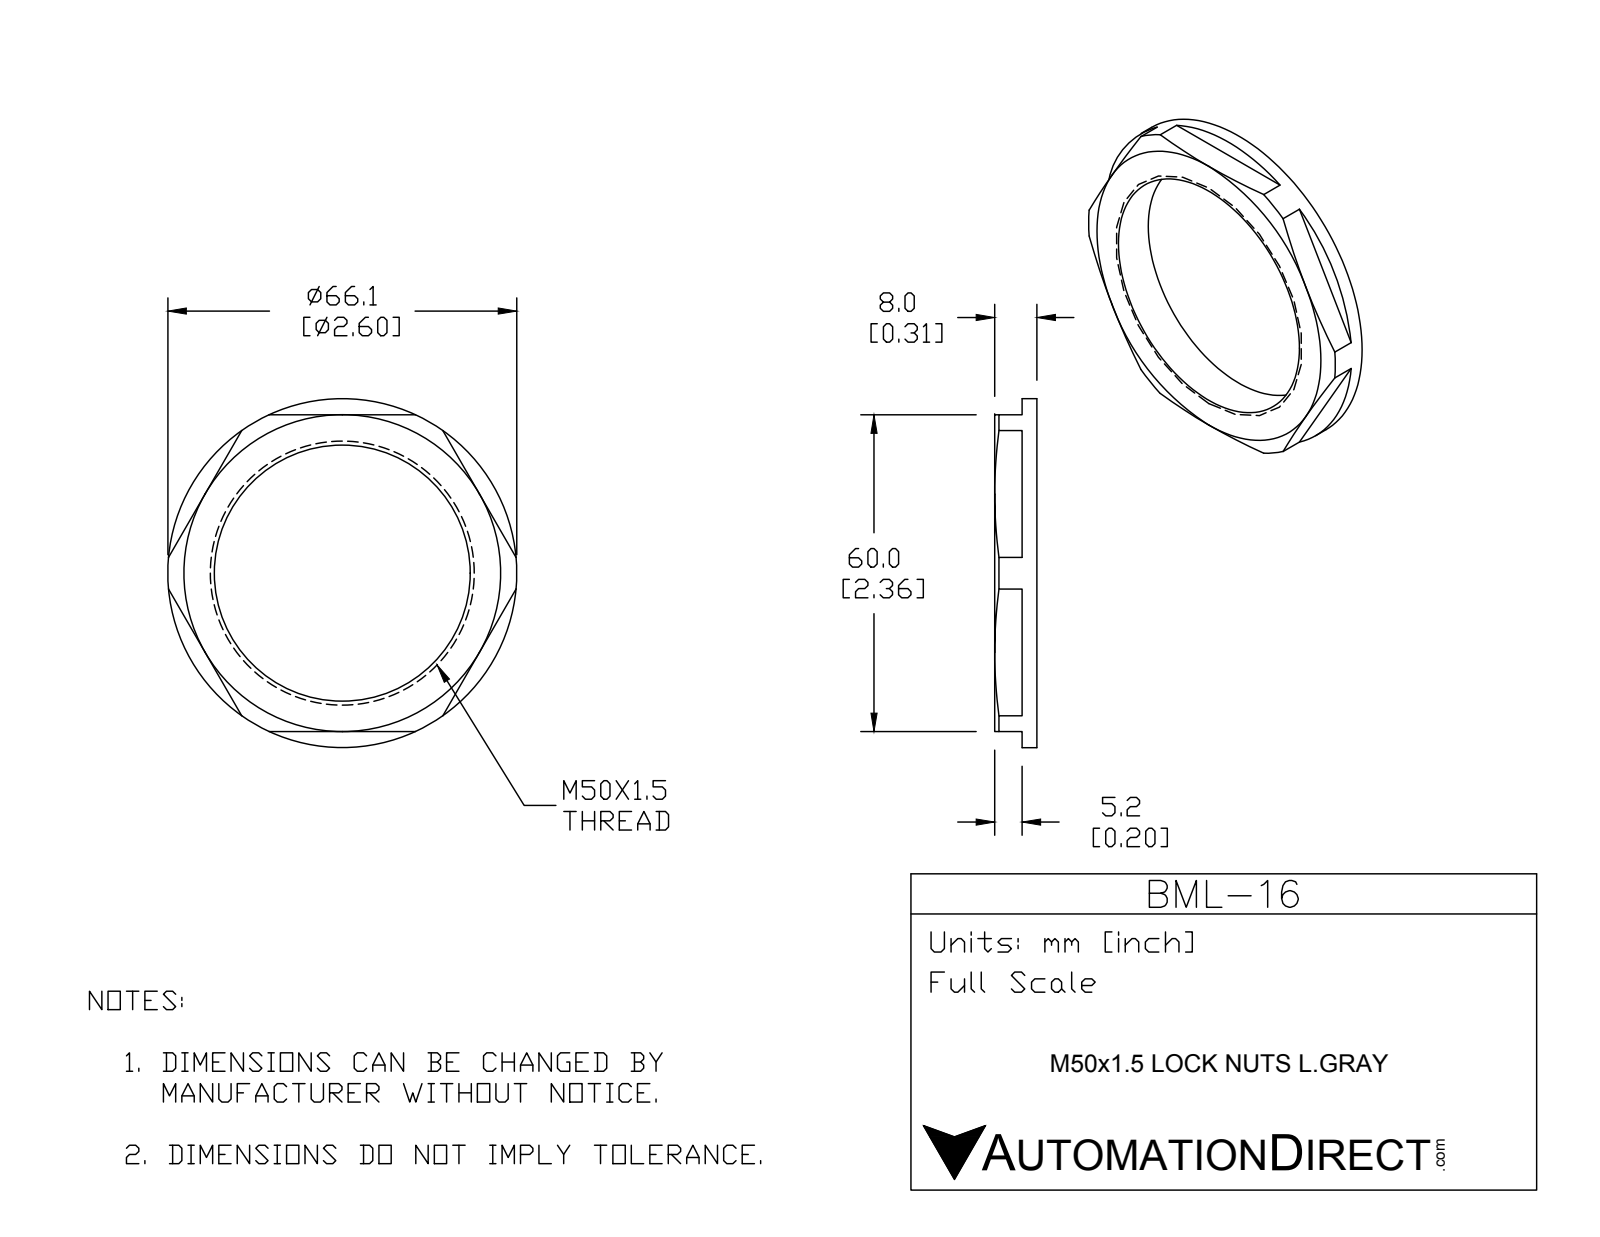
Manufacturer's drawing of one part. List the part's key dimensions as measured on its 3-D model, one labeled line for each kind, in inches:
Part name (STEP PRODUCT): BML-16
STEP written by: SolidWorks 2015 (CONFIG_CONTROL_DESIGN)
Units: inches
Bodies: 1 solid, 33 faces (17 planar, 10 cylindrical, 6 other)
Overall size (bounding box): 2.602 × 2.602 × 0.315
Volume: 0.66 in³ · Surface area: 9.236 in²
Round holes (diameter × count): ⌀0.059 ×3, ⌀1.909 ×1
Round bosses / shafts (diameter × count): ⌀2.602 ×1
Main face-to-face distances: 0.315, 2.362, 0.11, 0.205, 0.098, 0.303
Hole centre spacings: 1.244, 2.155, 2.155
